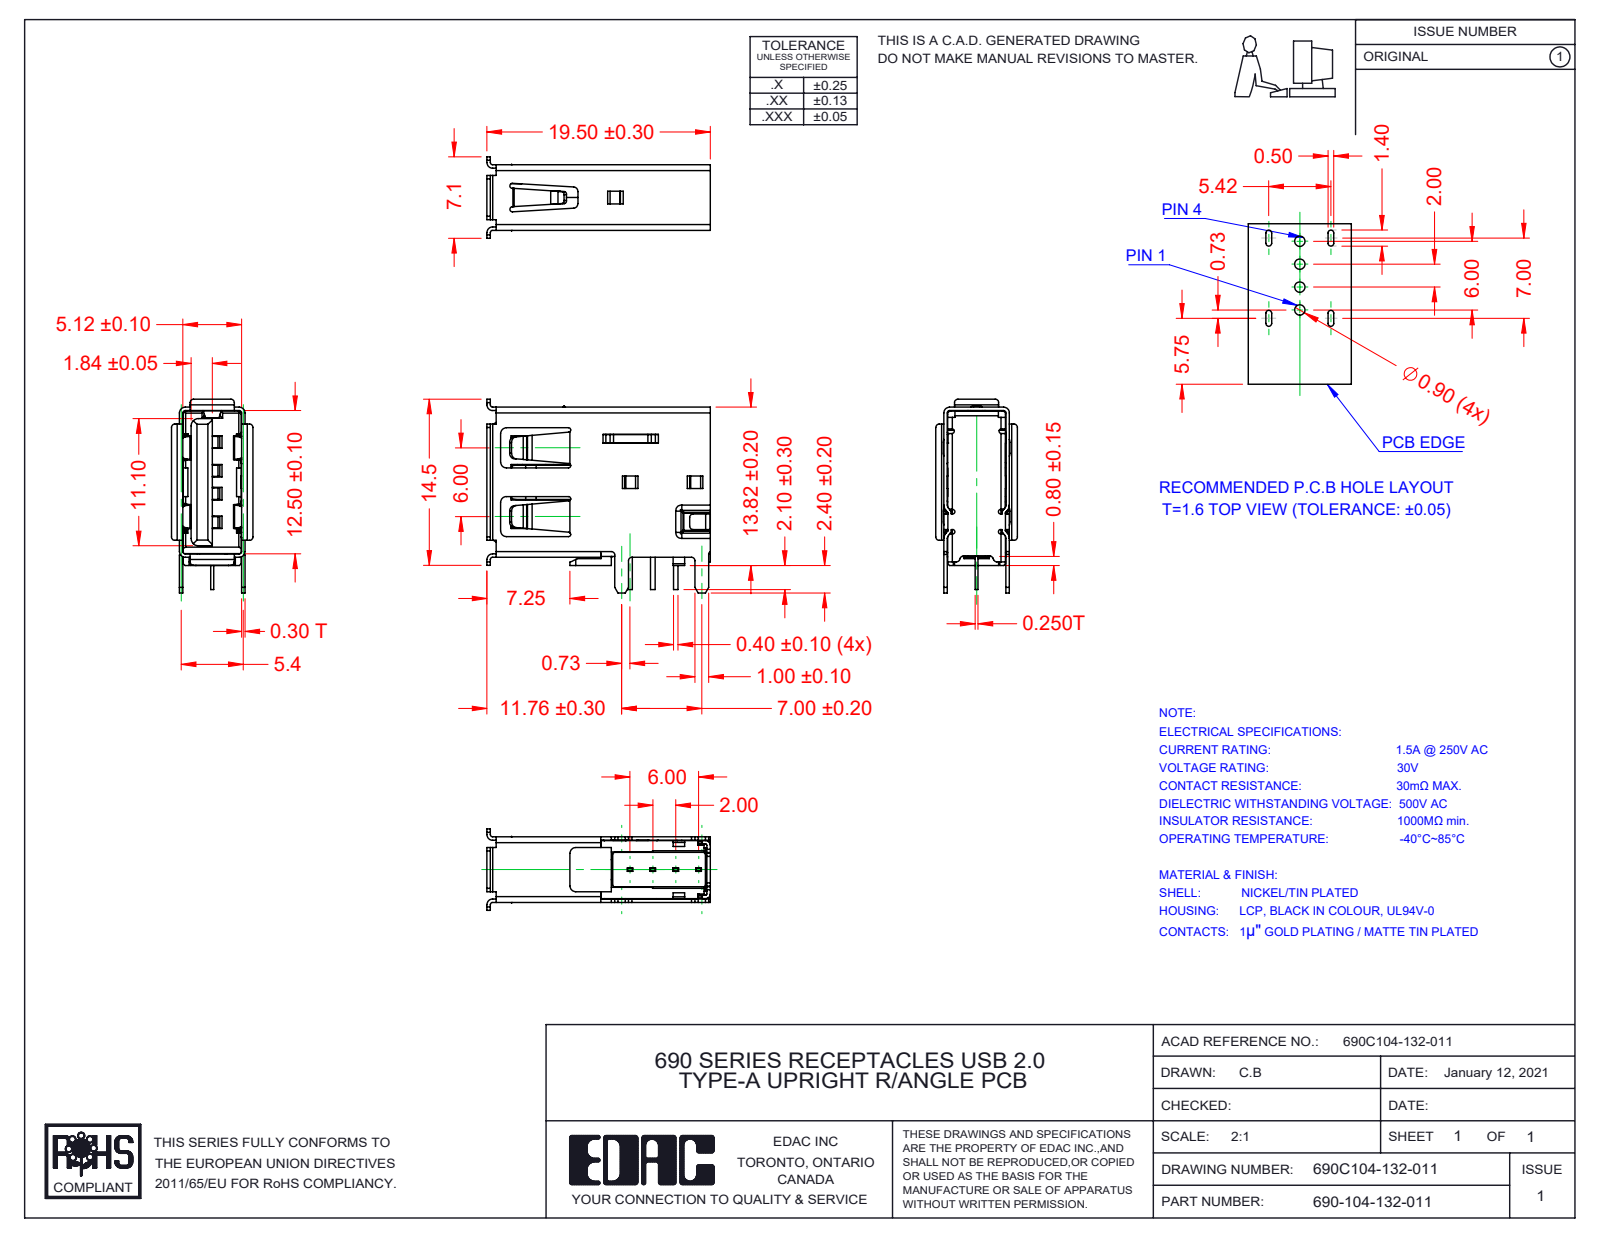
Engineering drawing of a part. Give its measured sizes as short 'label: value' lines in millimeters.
name: Shell 690C104-132-011; 690C104-132-011; Contacts 690C104-132-011; Insulator 690C104-132-011
written by: SolidWorks 2020 (AUTOMOTIVE_DESIGN)
unit: mm
bodies: 6 solids, 1161 faces (797 planar, 308 cylindrical, 56 other)
size: 19.5 × 16.92 × 7.12
volume: 631 mm³; area: 2 736 mm²
rounds: 50× R0.3, 26× R0.2, 25× R0.5, 24× R0.4, 23× R0.15, 18× R0.6, 15× R0.1, 11× R0.7
face distances: 5.42, 5.72, 5.12, 2.56, 2.86, 4.7, 2.5, 12.8, 1.1, 1.02
